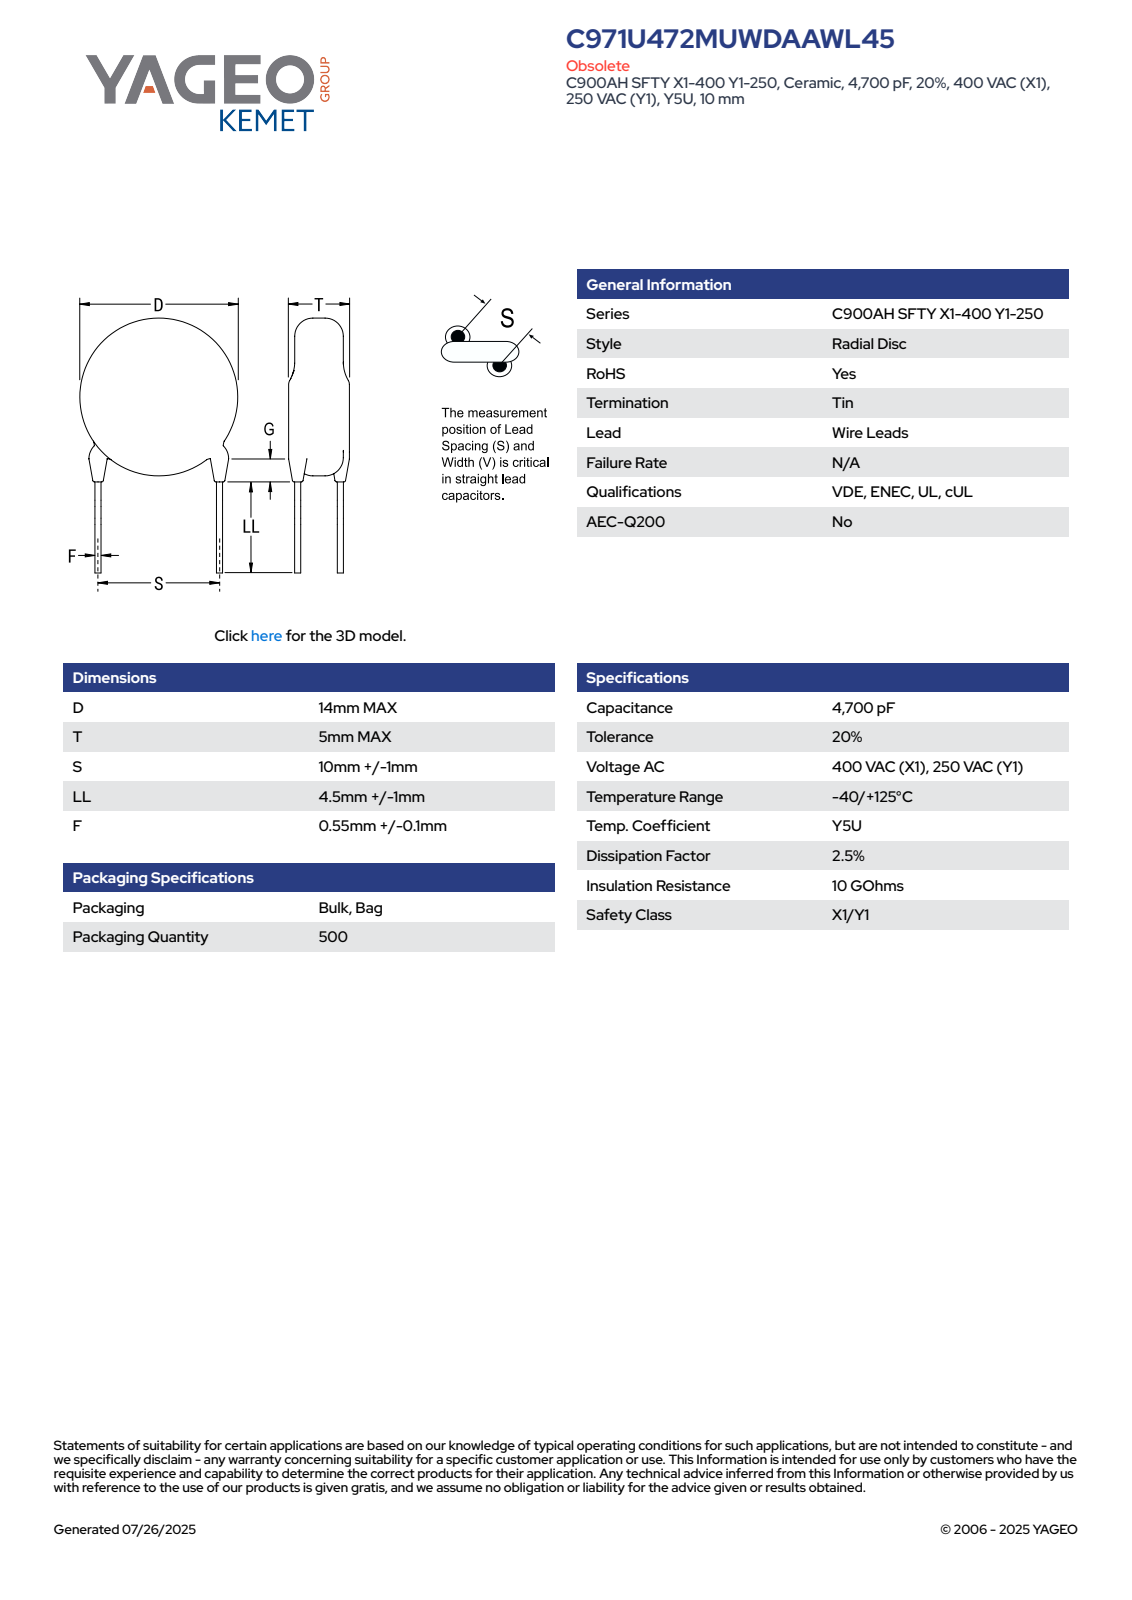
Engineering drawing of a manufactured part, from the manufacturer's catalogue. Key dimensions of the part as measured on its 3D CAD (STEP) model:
Part name (STEP PRODUCT): CCD_STC900_D14T5S10LL5.5F0.65G3
STEP written by: SolidWorks 2014 (AUTOMOTIVE_DESIGN)
Units: millimetres
Bodies: 4 solids, 83 faces (61 planar, 6 cylindrical, 16 other)
Overall size (bounding box): 19.79 × 14 × 5
Volume: 758 mm³ · Surface area: 537 mm²
Round bosses / shafts (diameter × count): ⌀0.65 ×2, ⌀14 ×1
Main face-to-face distances: 5, 13.59, 11.98, 1.61, 0.4, 6.61, 0.44, 0.6, 0.31, 1.3
